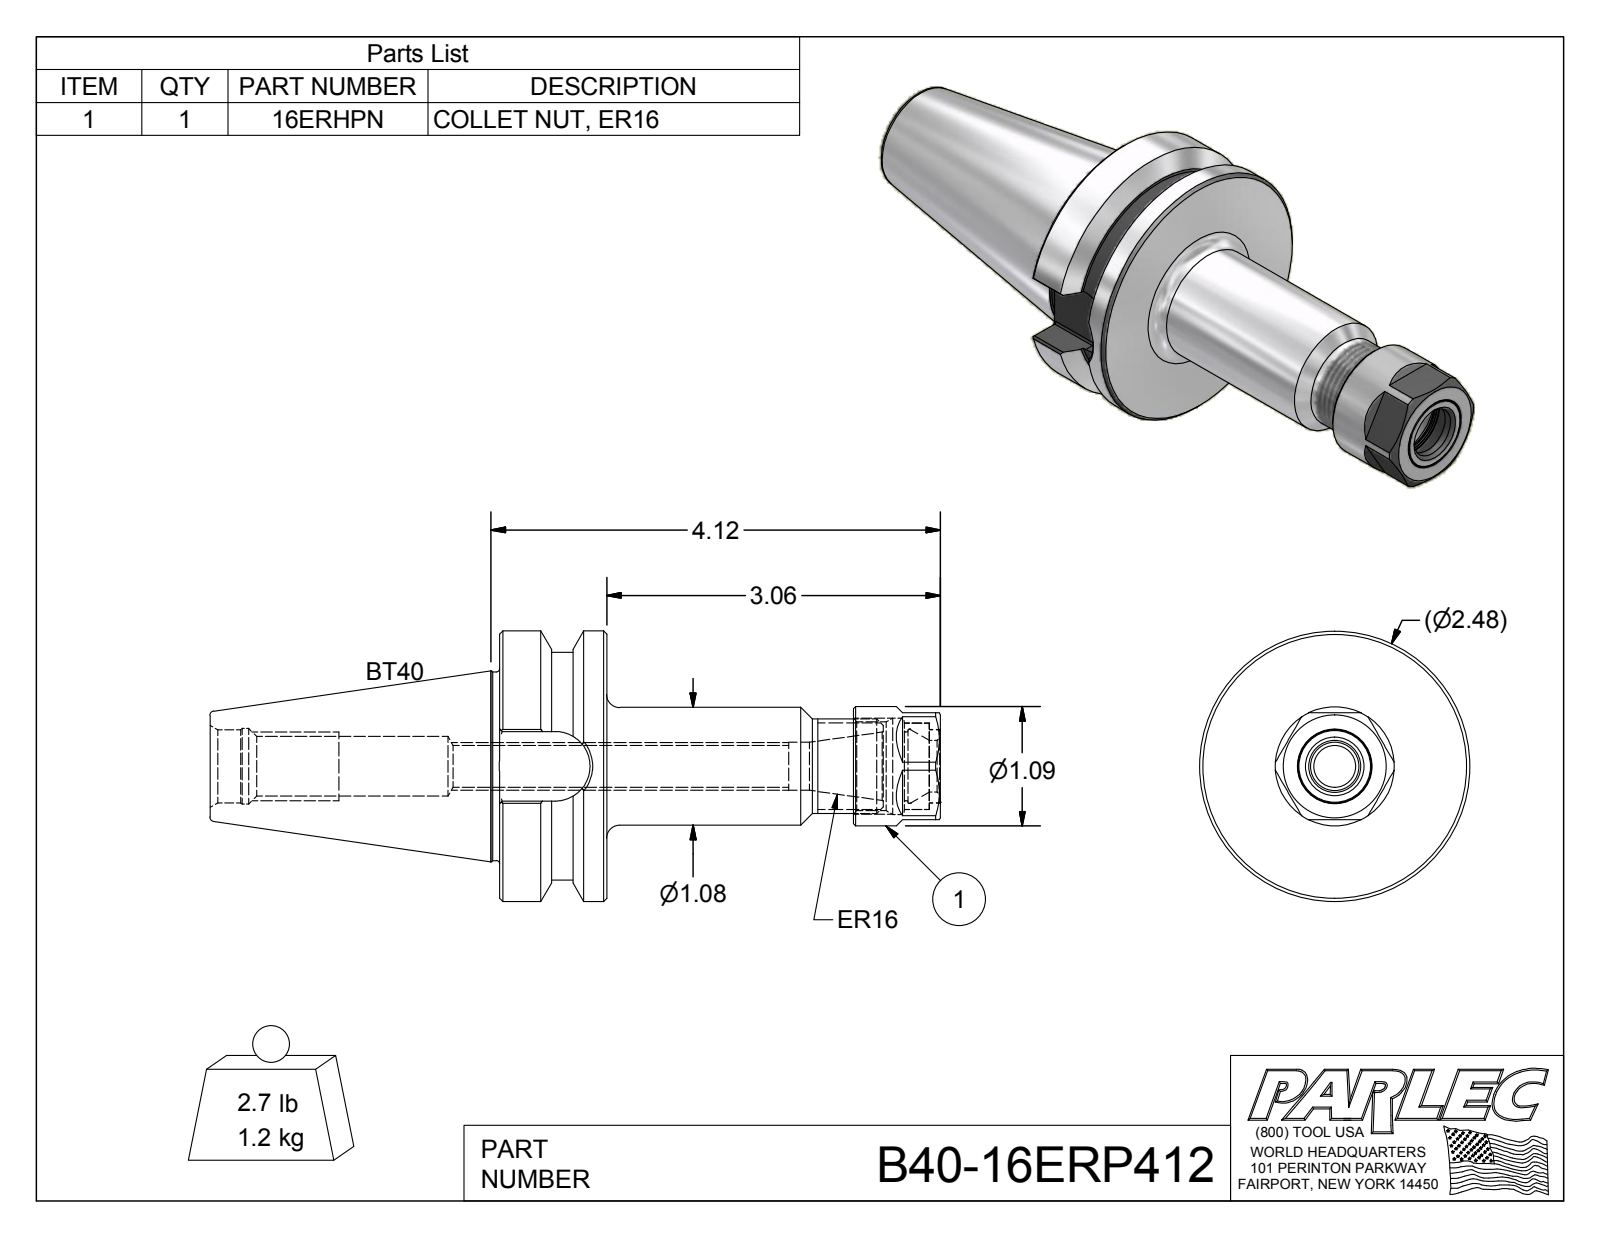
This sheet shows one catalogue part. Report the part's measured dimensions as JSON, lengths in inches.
{"part_name": "B40-16ERP412; B40-16ER4-1; 16ERHPN", "step_written_by": "Autodesk Inventor 2012 (AUTOMOTIVE_DESIGN)", "units": "inches", "bodies": {"solids": 3, "faces": 114, "planar": 44, "cylindrical": 33, "other": 37}, "overall_size": [6.695, 2.48, 2.48], "volume_in3": 9.538, "surface_area_in2": 52.52, "round_holes": [[0.383, 1], [0.44, 1], [0.474, 1], [0.545, 1], [0.63, 1], [0.67, 1], [0.674, 1], [0.68, 1], [0.694, 1], [0.794, 1], [0.814, 1], [0.883, 1]], "round_bosses_or_shafts": [[2.48, 1], [2.087, 1], [1.73, 1], [1.092, 1], [1.08, 1], [0.866, 1], [0.79, 1], [0.67, 1]], "partial_cylinders_radius": [[0.02, 8], [0.319, 1]], "face_to_face_distances": [0.984, 0.98, 1.78, 4.042, 3.058, 0.172, 0.809, 3.246, 2.262, 0.796]}
